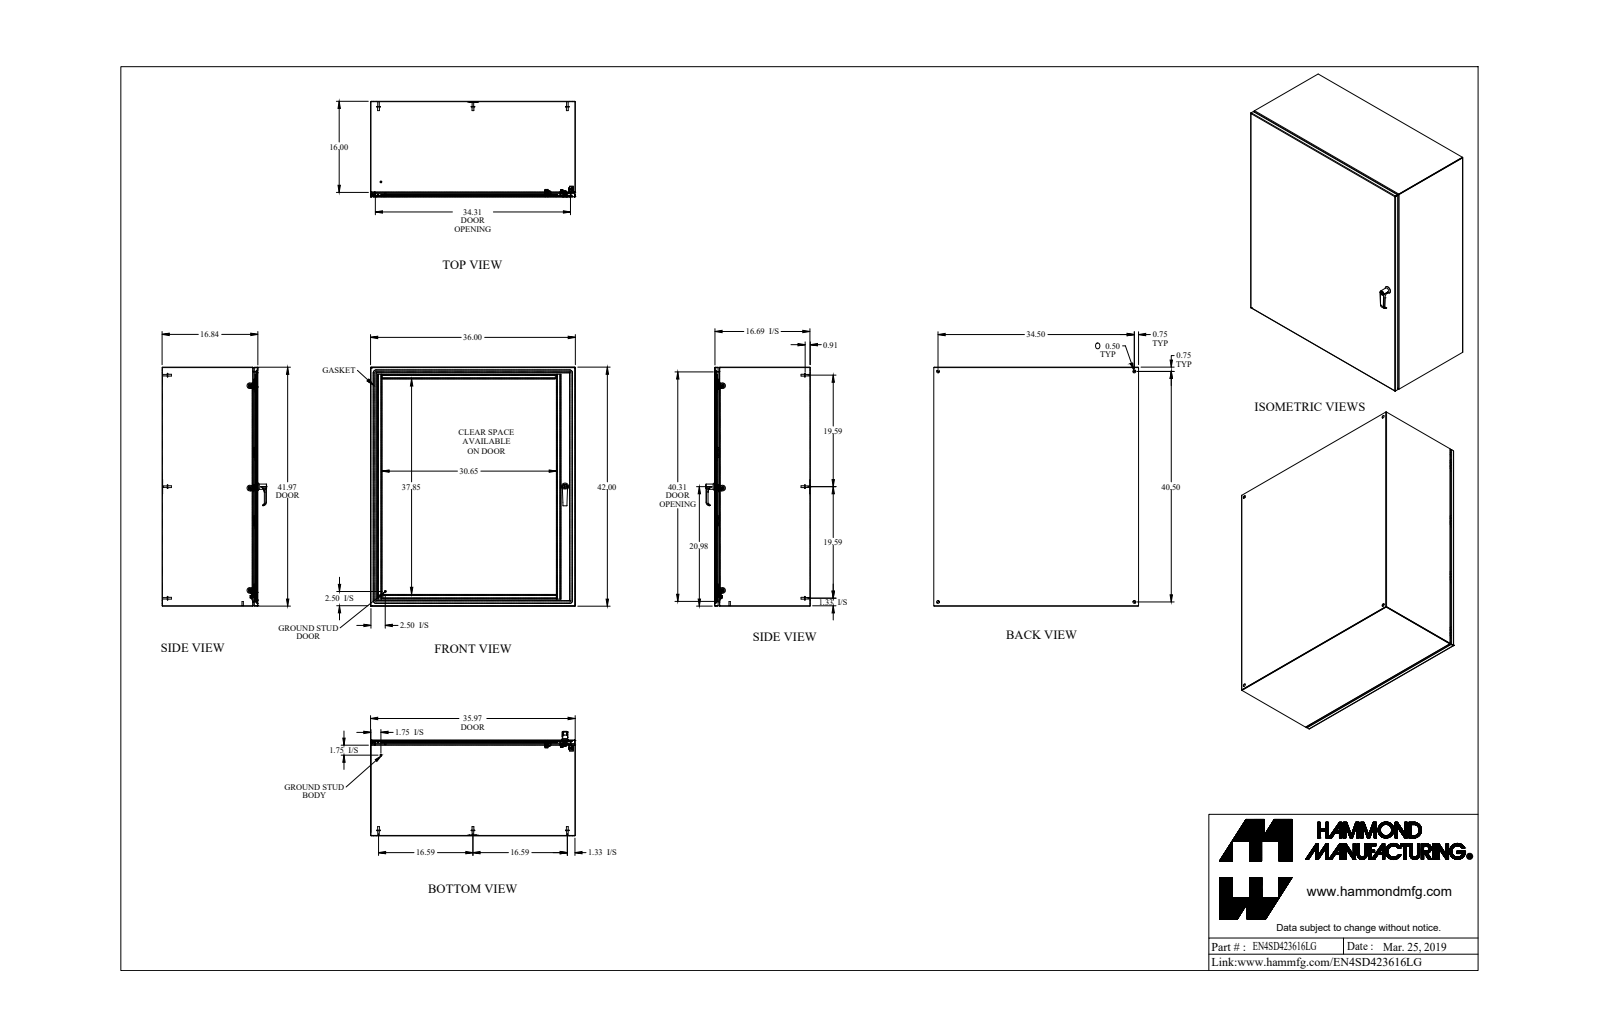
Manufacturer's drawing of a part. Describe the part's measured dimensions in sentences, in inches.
The part is named "EN4SD423616LG". Its 3-D file was written by "SolidWorks 2018 (AUTOMOTIVE_DESIGN)". It is 63 solids with 1719 faces: 757 planar, 632 cylindrical and 330 other. Overall it measures 42 by 36 by 18.367 inches. Its volume is 453.6 cubic inches and its surface area 12 688 square inches. Round holes: 6 of diameter 0.176, 4 of diameter 0.196, 4 of diameter 0.5, 3 of diameter 0.25, 3 of diameter 0.265, 3 of diameter 0.413, 2 of diameter 0.256, 2 of diameter 0.313, 2 of diameter 0.394, 1 of diameter 0.172, 1 of diameter 0.24, 1 of diameter 0.242. Round bosses or shafts: 8 of diameter 0.313, 8 of diameter 0.27, 7 of diameter 0.625, 7 of diameter 0.25, 6 of diameter 0.375, 6 of diameter 0.156, 3 of diameter 1, 2 of diameter 0.63. Partial cylindrical surfaces (rounded edges, fillets, slot ends): 24 of radius 0.043, 24 of radius 0.081, 18 of radius 0.036, 18 of radius 0.108, 15 of radius 0.03, 13 of radius 0.062, 10 of radius 0.094, 9 of radius 0.016. The main face-to-face distances are 0.072, 16.765, 16.693, 16.837, 35.928, 41.928, 35.856, 36, 41.856, 42. The hole center spacings are 35.969, 0.787, 18, 33.504, 34.5, 40.5, 53.202, 0.013.
